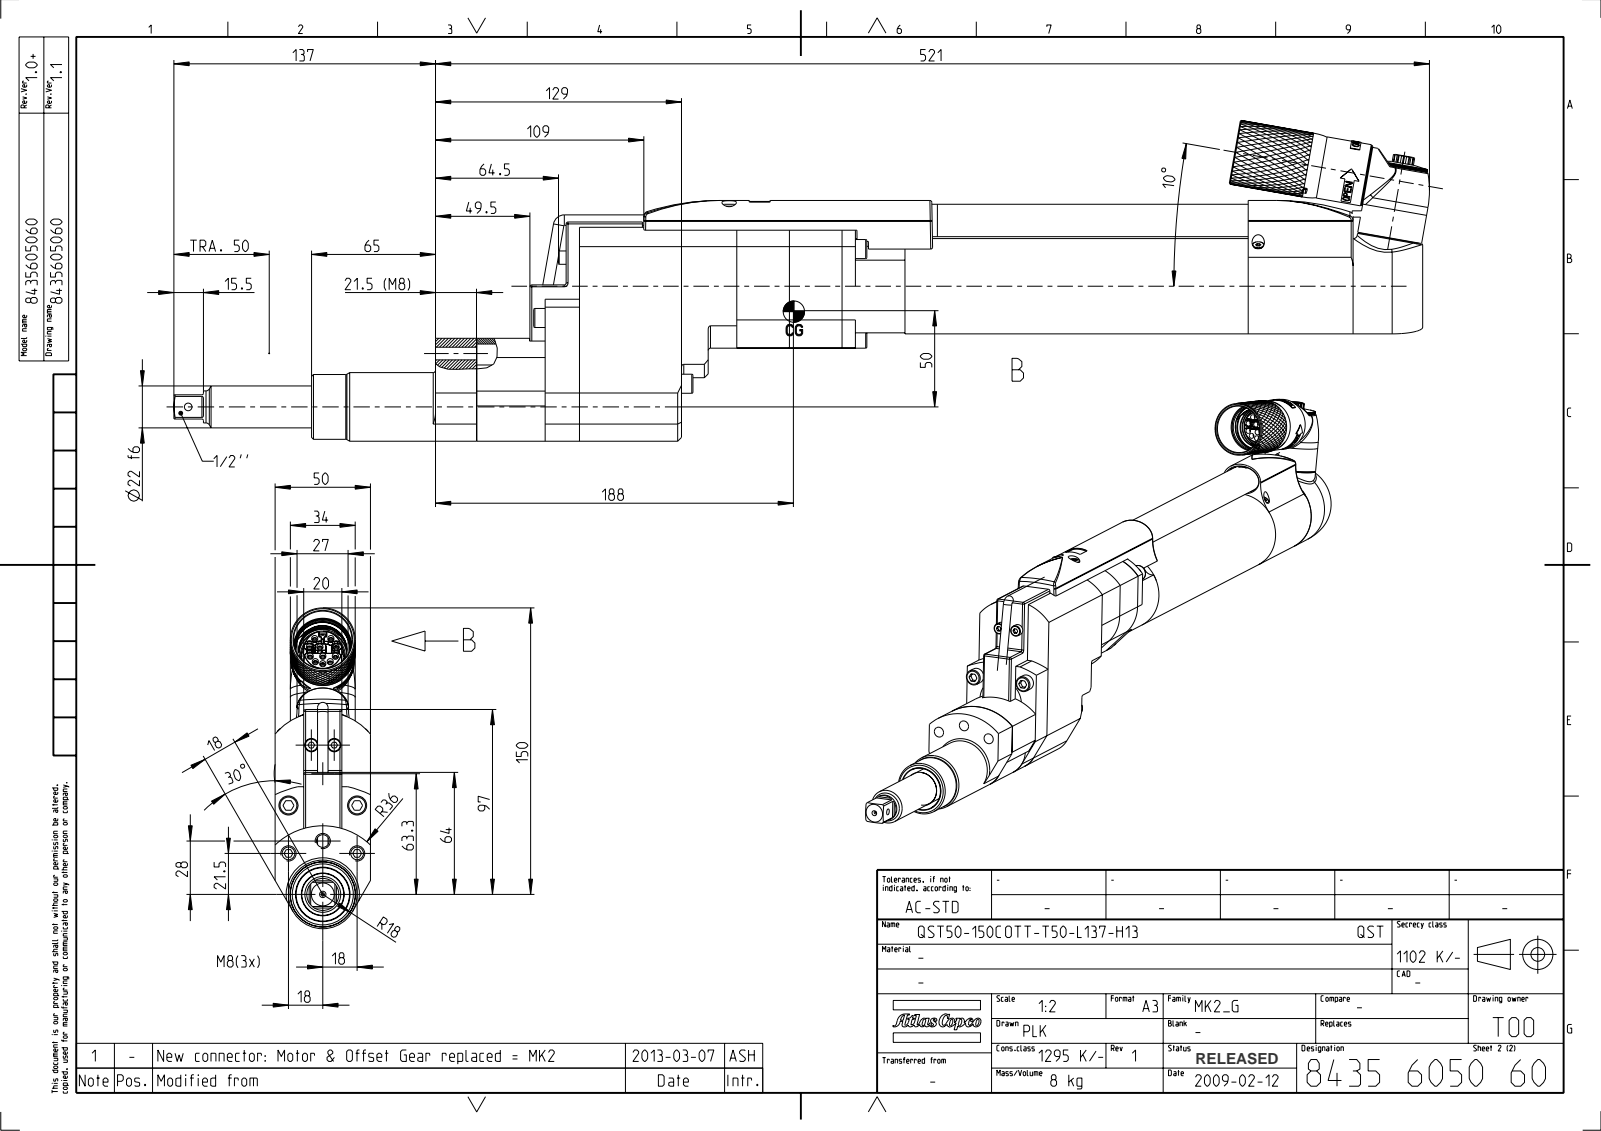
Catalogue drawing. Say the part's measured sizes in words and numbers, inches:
The part is named "EXT_COMP_SW0010". Its 3-D file was written by "CREO PARAMETRIC BY PTC INC, 2022414 (AP242_MANAGED_MODEL_BASED_3D_ENGINEERING_MIM_LF)". It is 1 solid with 1509 faces: 718 planar, 344 cylindrical and 447 other. Overall it measures 25.923 by 6.627 by 1.988 inches. Its volume is 92.67 cubic inches and its surface area 289.6 square inches. Round holes: 4 of diameter 0.128, 4 of diameter 0.138, 4 of diameter 0.177, 4 of diameter 0.217, 3 of diameter 0.262, 2 of diameter 0.097, 2 of diameter 0.115, 2 of diameter 0.167, 2 of diameter 0.256, 2 of diameter 0.354, 1 of diameter 0.063, 1 of diameter 0.157. Round bosses or shafts: 7 of diameter 0.394, 4 of diameter 0.276, 4 of diameter 0.157, 3 of diameter 1.339, 3 of diameter 0.118, 2 of diameter 0.22, 1 of diameter 1.969, 1 of diameter 1.417. Partial cylindrical surfaces (rounded edges, fillets, slot ends): 18 of radius 0.039, 12 of radius 0.011, 12 of radius 0.02, 6 of radius 0.031, 4 of radius 1.22, 3 of radius 0.079, 3 of radius 0.236, 3 of radius 1.28. The main face-to-face distances are 1.969, 0.039, 0.591, 0.748, 0.709, 1.378, 0.787, 1.339, 0.63, 17.409. The hole center spacings are 0.472, 1.417, 0.591, 0.754, 0.754, 0.756, 0.923, 1.077.
